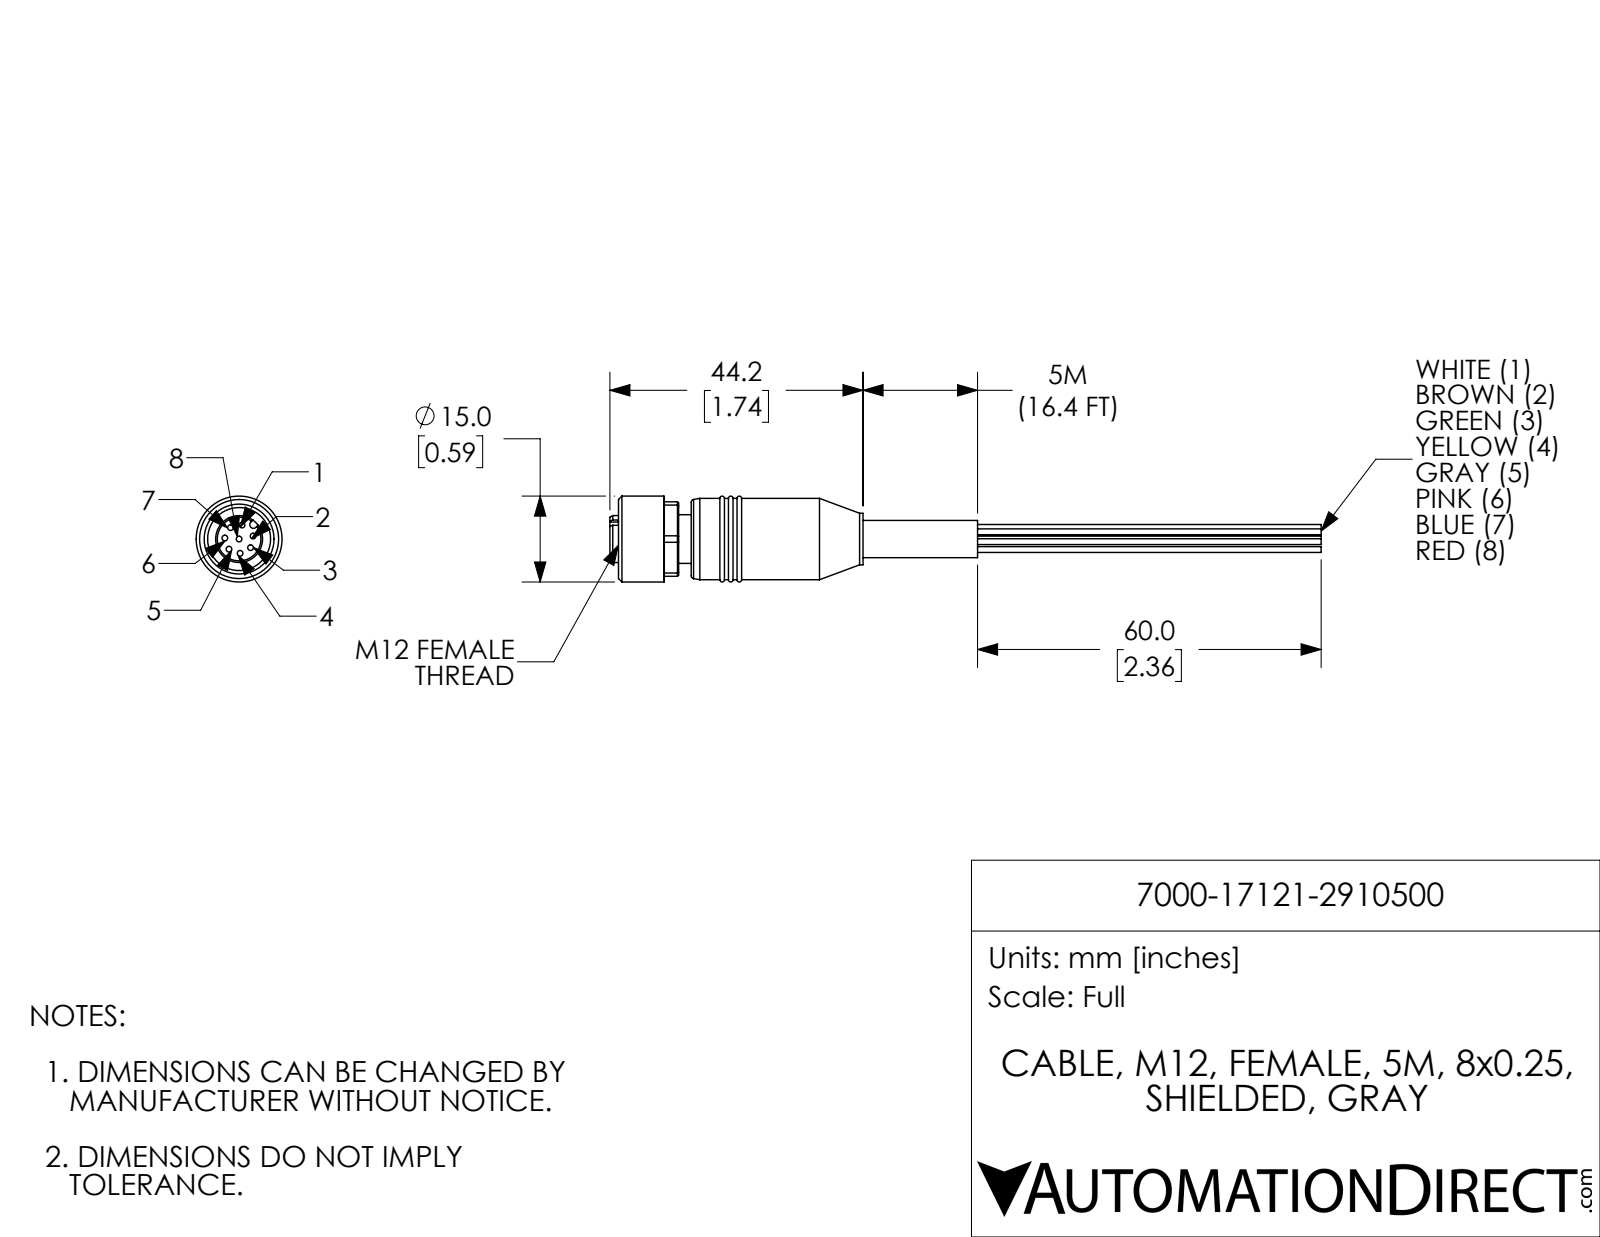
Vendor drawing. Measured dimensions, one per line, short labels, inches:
name: 7000-17121-2910500
written by: SolidWorks 2017 (AUTOMOTIVE_DESIGN)
unit: in
bodies: 1 solid, 131 faces (39 planar, 59 cylindrical, 33 other)
size: 4.89 × 0.591 × 0.591
volume: 0.428 in³; area: 7.634 in²
holes: 8× ⌀0.039, 1× ⌀0.433
bosses: 8× ⌀0.04, 1× ⌀0.591, 1× ⌀0.559, 1× ⌀0.354, 1× ⌀0.335, 1× ⌀0.323, 1× ⌀0.256
rounds: 1× R0.026, 1× R0.283
face distances: 0.087, 0.512, 0.118, 0.205, 0.354, 0.472, 0.559, 0.098, 0.059, 0.295
hole spacings: 0.098, 0.081, 0.149, 0.195, 0.082, 0.166, 0.189, 0.189
